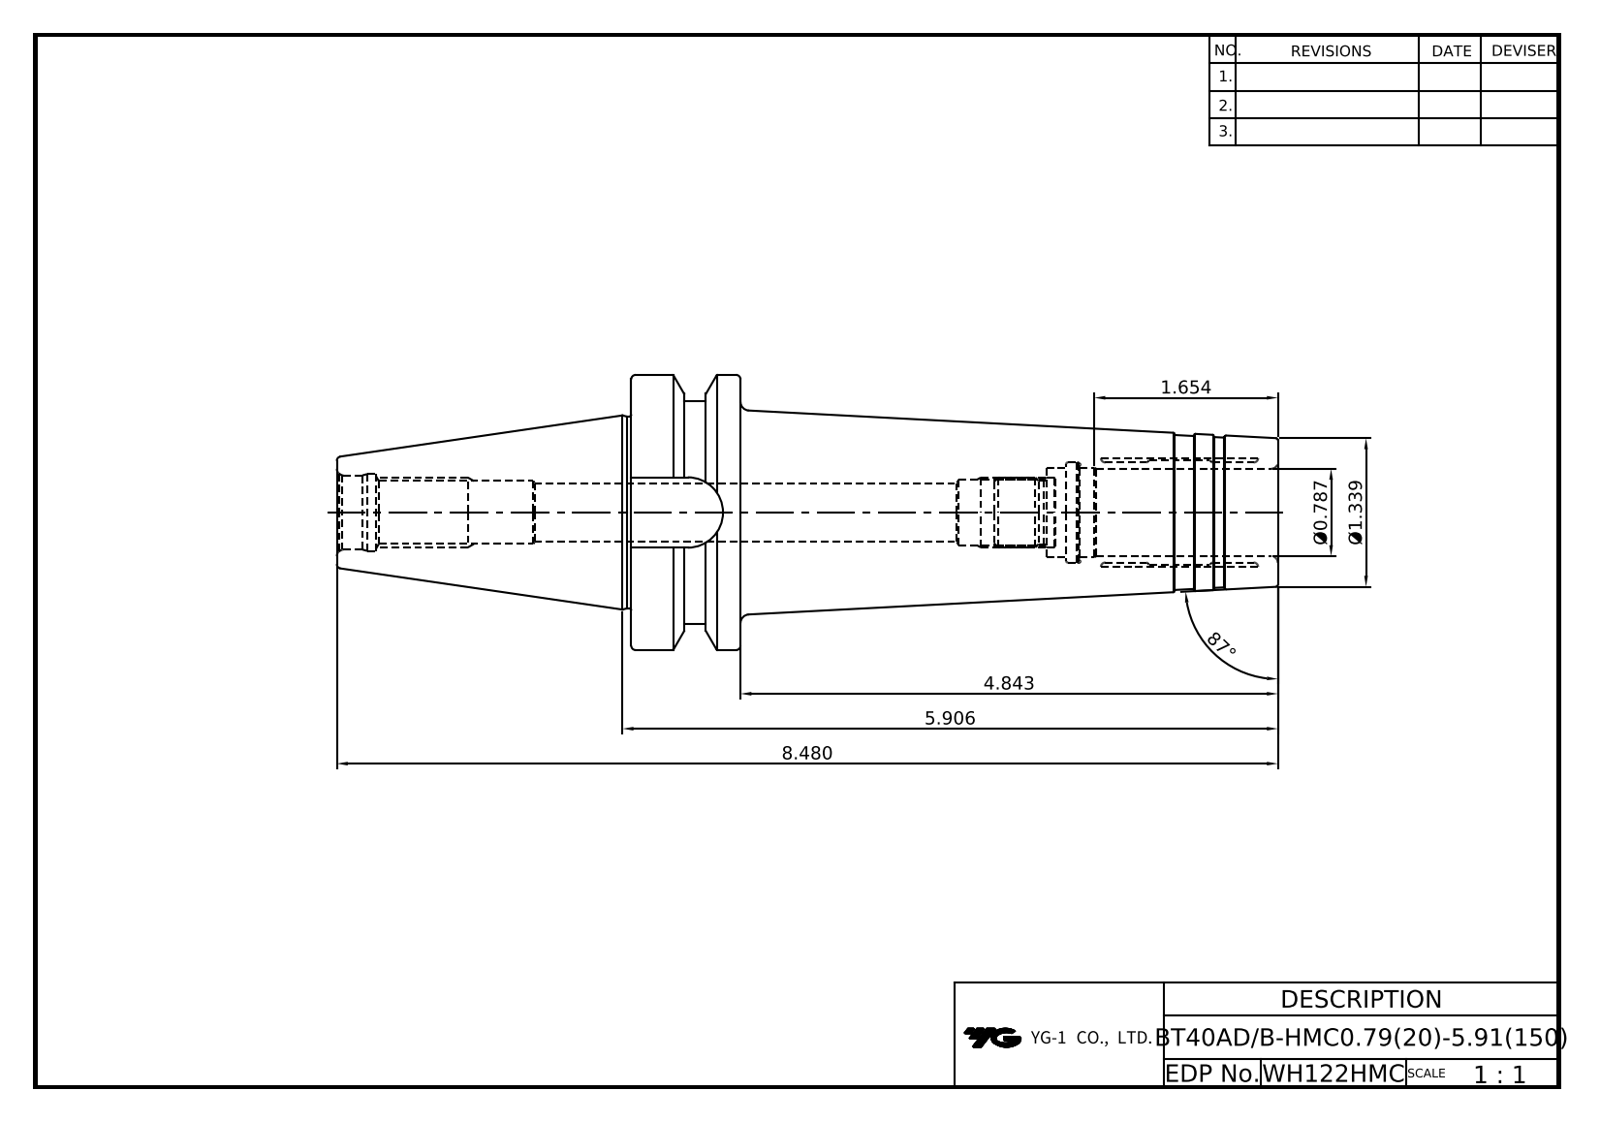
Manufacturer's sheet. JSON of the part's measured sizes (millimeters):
{"part_name": "BT40ADB-HMC20-150", "step_written_by": "Autodesk Inventor 2020 (AUTOMOTIVE_DESIGN)", "units": "millimeters", "bodies": {"solids": 1, "faces": 84, "planar": 21, "cylindrical": 27, "other": 36}, "overall_size": [215.4, 63, 63], "volume_mm3": 250363, "surface_area_mm2": 44469, "round_holes": [[3.24, 4], [4, 4], [13.5, 1], [13.84, 1], [14.92, 1], [17, 1], [17.6, 1], [20, 1], [20.4, 1]], "round_bosses_or_shafts": [[63, 1], [51, 1], [44, 1]], "partial_cylinders_radius": [[8.05, 1]], "face_to_face_distances": [25, 148, 123, 45.2, 17.1, 7.9, 130.9, 12.1, 5, 12.9]}
